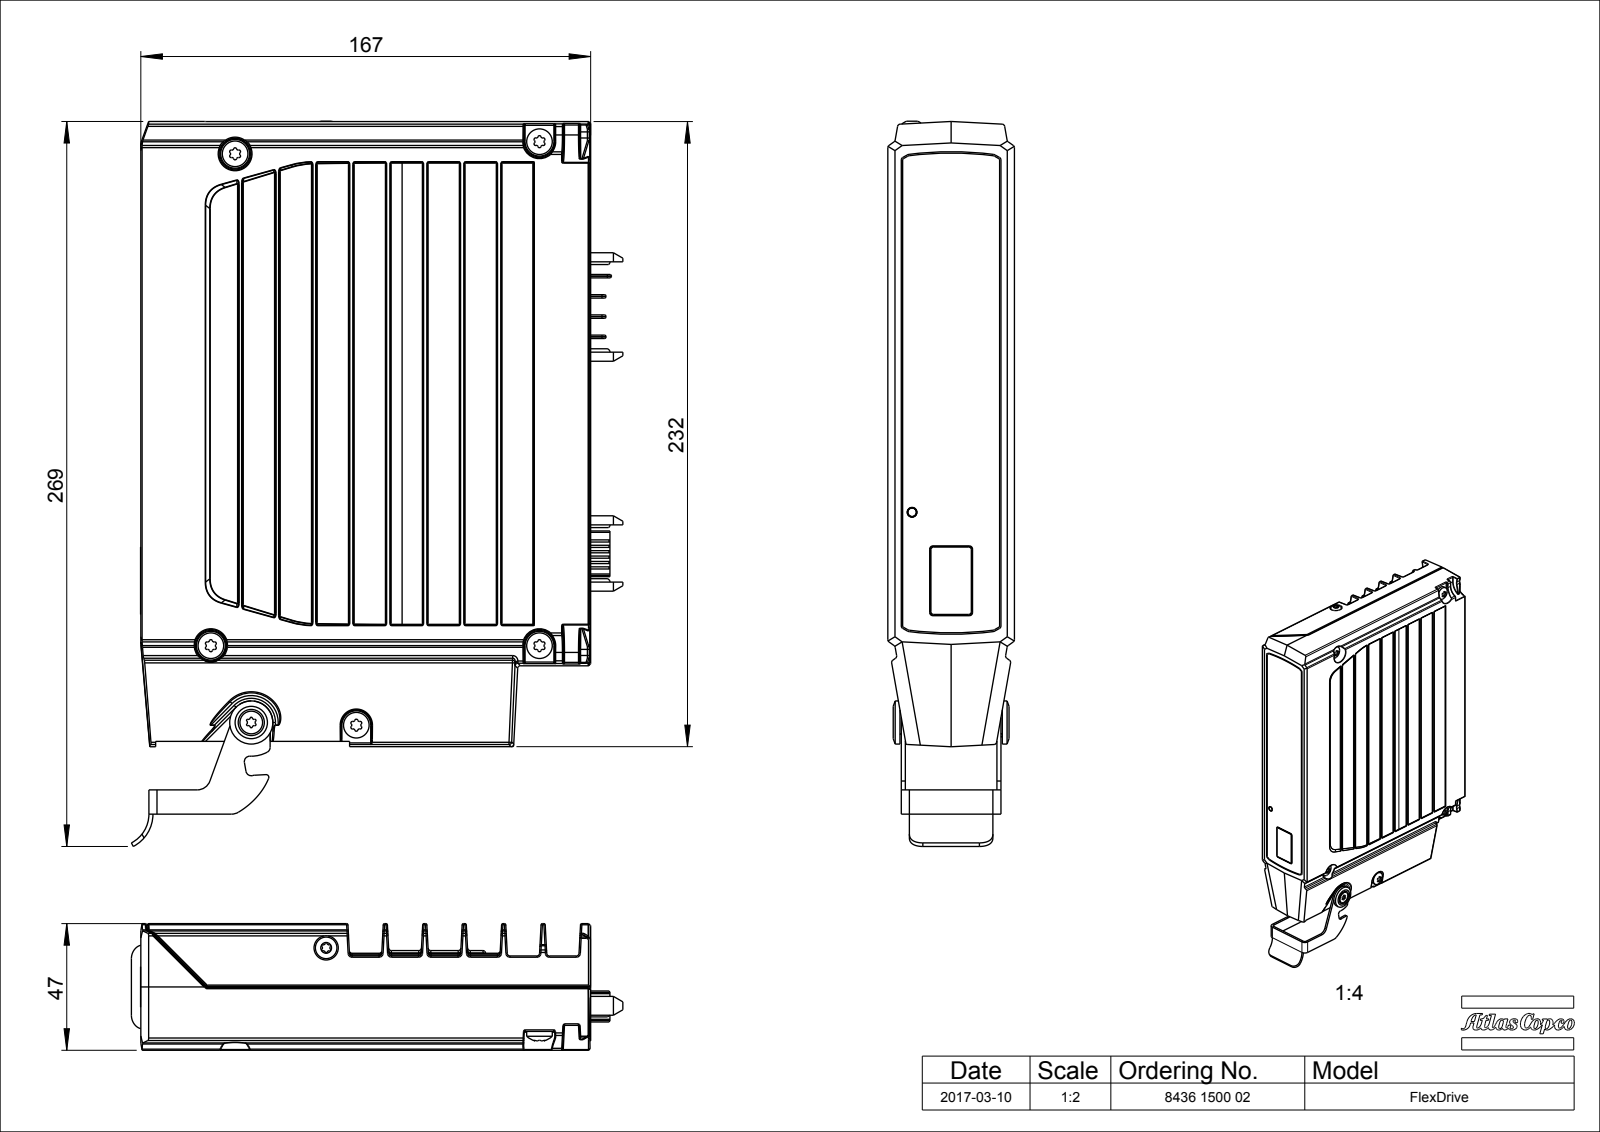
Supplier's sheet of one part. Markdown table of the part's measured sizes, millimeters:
| quantity | value |
| --- | --- |
| part name | 4222204510; 4222201180_1; 4222201180_DESIGN_ASM; 4222199700 (+8 more) |
| STEP written by | CREO PARAMETRIC BY PTC INC, 2020281 (CONFIG_CONTROL_DESIGN) |
| units | millimeters |
| bodies | 21 solids, 12341 faces (4802 planar, 3779 cylindrical, 3760 other) |
| overall size | 269.1 × 182.45 × 47 |
| volume | 712 208 mm³ |
| surface area | 590 604 mm² |
| round holes (diameter × count) | 4.22 × 3, 2.7 × 1, 3 × 1, 3.24 × 1, 3.3 × 1, 4 × 1, 4.2 × 1, 4.5 × 1, 5.4 × 1, 8.1 × 1, 9 × 1 |
| round bosses / shafts (diameter × count) | 1 × 39, 9.5 × 5, 5 × 5, 8 × 2, 16 × 1, 8.4 × 1, 7.9 × 1, 5.38 × 1 |
| partial cylindrical surfaces (radius × count) | 1 × 577, 0.3 × 354, 0.5 × 238, 0.1 × 77, 0.58 × 60, 0.1 × 32, 0.13 × 26, 1.02 × 16 |
| main face-to-face distances | 3, 8.5, 44, 18.5, 10, 25.5, 35.5, 2, 12, 14.63 |
| hole center spacings | 64.53, 13.15, 16.42, 23, 24.7, 38.07, 43.09, 51.39 |
